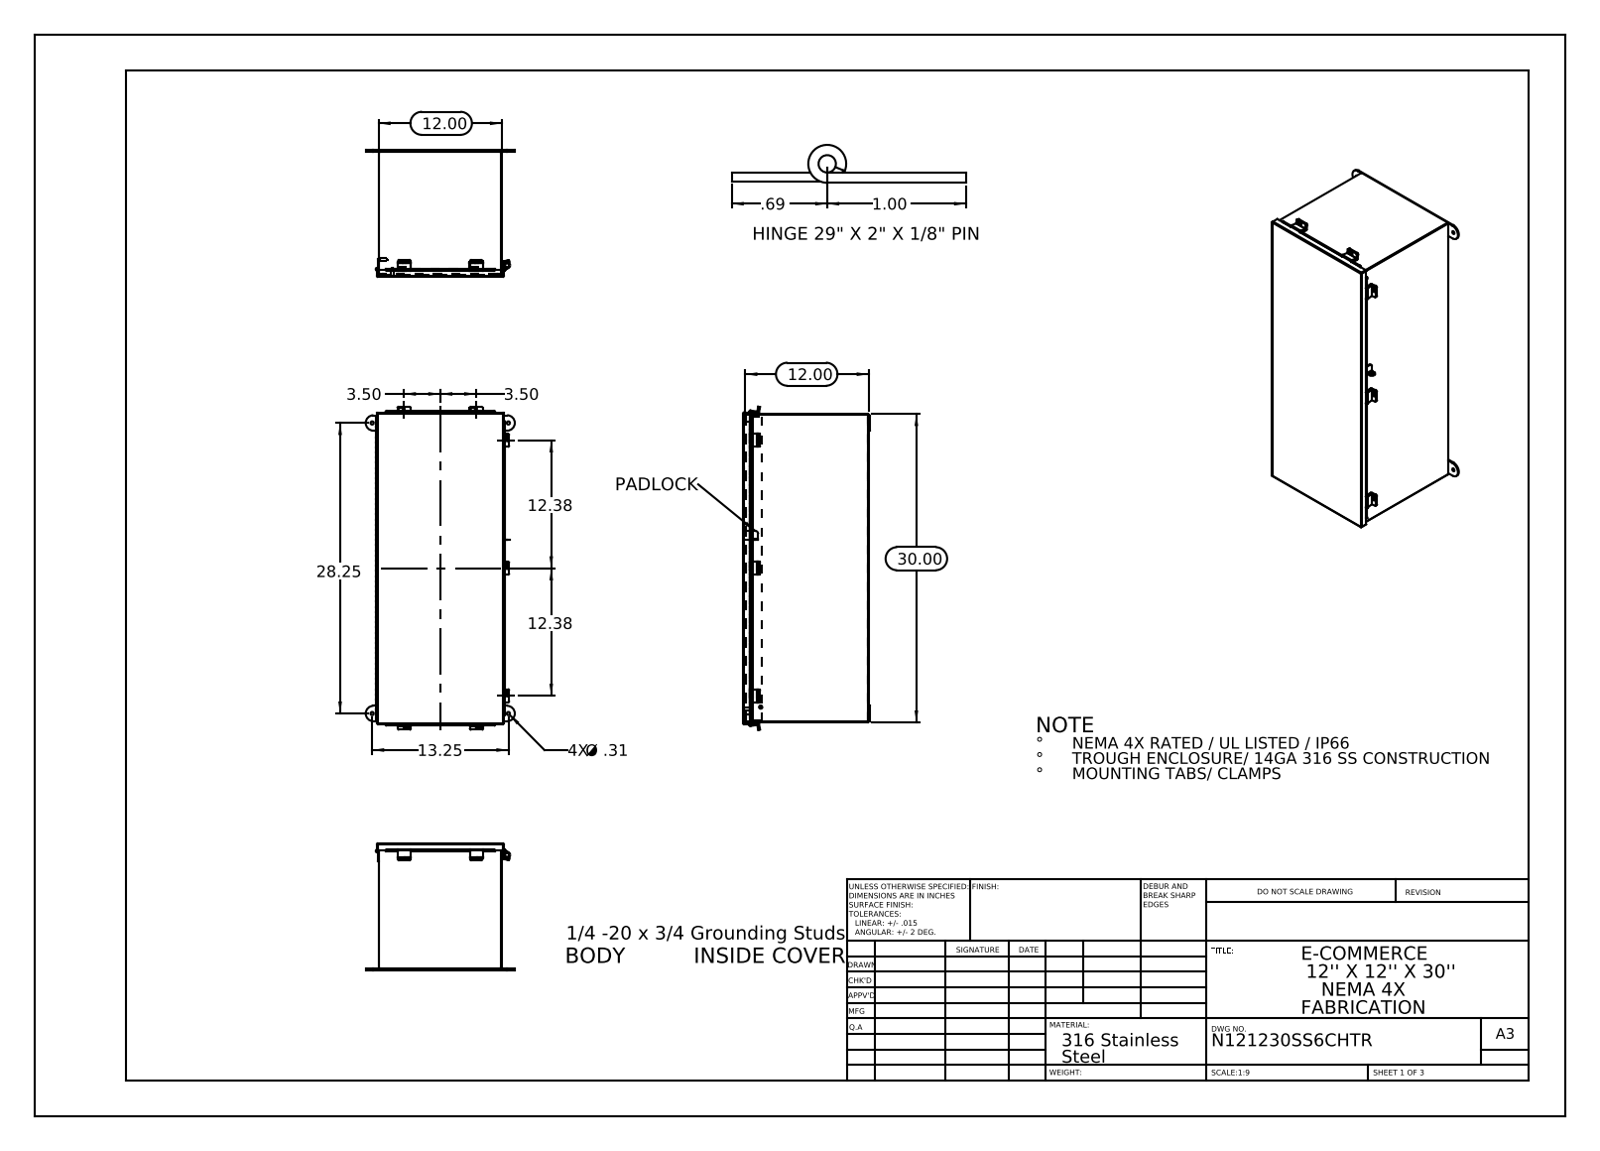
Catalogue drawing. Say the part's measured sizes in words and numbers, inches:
The part is named "N121230SSCHTR Hinge Cover Side JIC; HW-CLH-JH-20154; N121230SSCHTR JIC_Cover_Template; N121230SSCHTR (+8 more)". Its 3-D file was written by "SolidWorks 2013 (CONFIG_CONTROL_DESIGN)". It is 25 solids with 1098 faces: 677 planar, 401 cylindrical and 20 other. Overall it measures 31.407 by 14.5 by 12.337 inches. Its volume is 146.7 cubic inches and its surface area 3 915 square inches. Round holes: 7 of diameter 0.25, 4 of diameter 0.313, 1 of diameter 0.125, 1 of diameter 0.375. Round bosses or shafts: 2 of diameter 0.315, 2 of diameter 0.236, 1 of diameter 0.273, 1 of diameter 0.25. Partial cylindrical surfaces (rounded edges, fillets, slot ends): 26 of radius 0.125, 14 of radius 0.133, 12 of radius 0.009, 10 of radius 0.013, 10 of radius 0.088, 6 of radius 0.083, 6 of radius 0.1, 4 of radius 0.75. The main face-to-face distances are 0.075, 11.925, 12.128, 11.85, 12, 12.203, 12.053, 29.925, 29.85, 30. The hole center spacings are 7, 12.425, 13.25, 28.25, 31.203, 12.632, 24.85.
